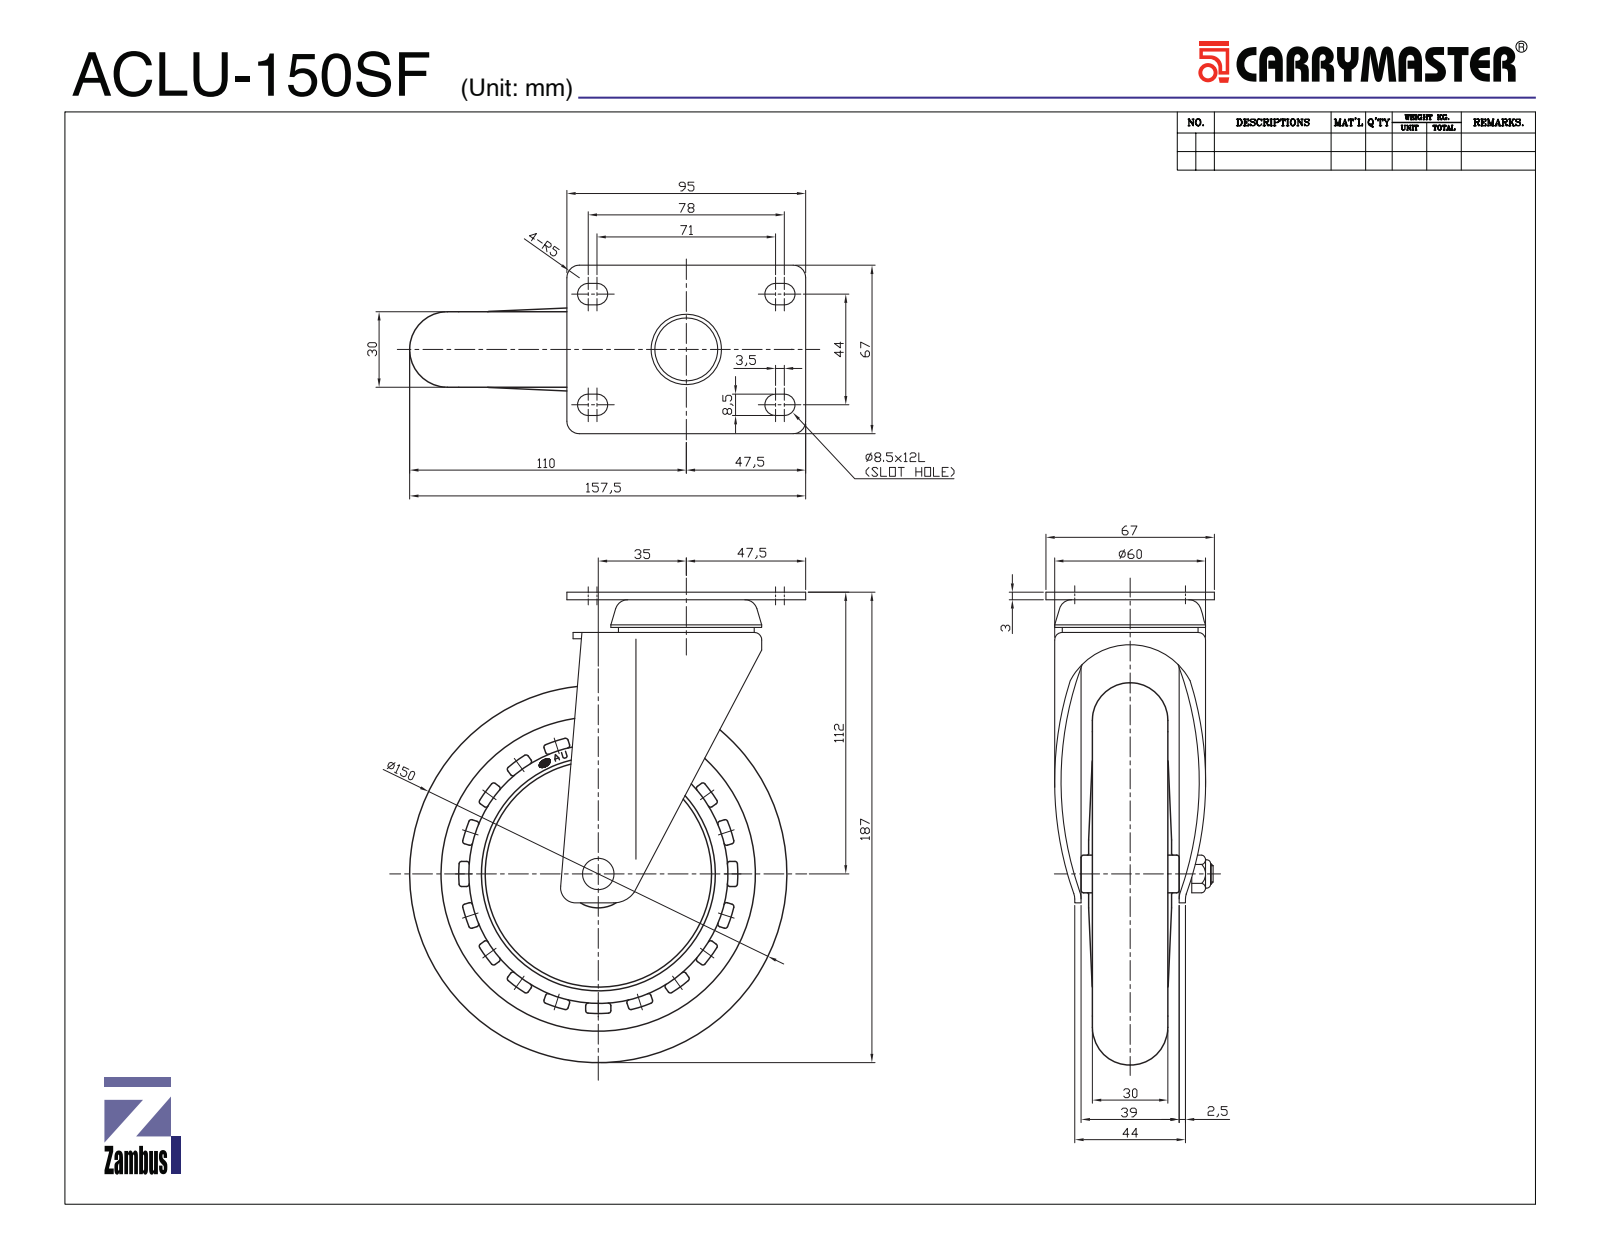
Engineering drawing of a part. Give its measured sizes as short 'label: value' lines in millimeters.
name: ACLU-150SF
written by: SolidWorks 2015 (CONFIG_CONTROL_DESIGN)
unit: mm
bodies: 14 solids, 986 faces (462 planar, 262 cylindrical, 262 other)
size: 186 × 158.42 × 69.31
volume: 457 762 mm³; area: 180 448 mm²
holes: 1× ⌀6.8, 1× ⌀8, 1× ⌀9.6, 1× ⌀12.6, 1× ⌀19.6, 1× ⌀22, 1× ⌀28.62, 1× ⌀29.82, 1× ⌀39.2, 1× ⌀88, 1× ⌀92, 1× ⌀103
bosses: 1× ⌀120, 1× ⌀90, 1× ⌀59.7, 1× ⌀32, 1× ⌀21.5, 1× ⌀16, 1× ⌀13, 1× ⌀12.5
rounds: 88× R1, 19× R3.86, 16× R46.25, 4× R5, 4× R6, 2× R1.5, 2× R2.5, 2× R7
face distances: 30.5, 12.3, 18.7, 0.5, 11.8, 18.2, 5, 2.5, 3, 31
